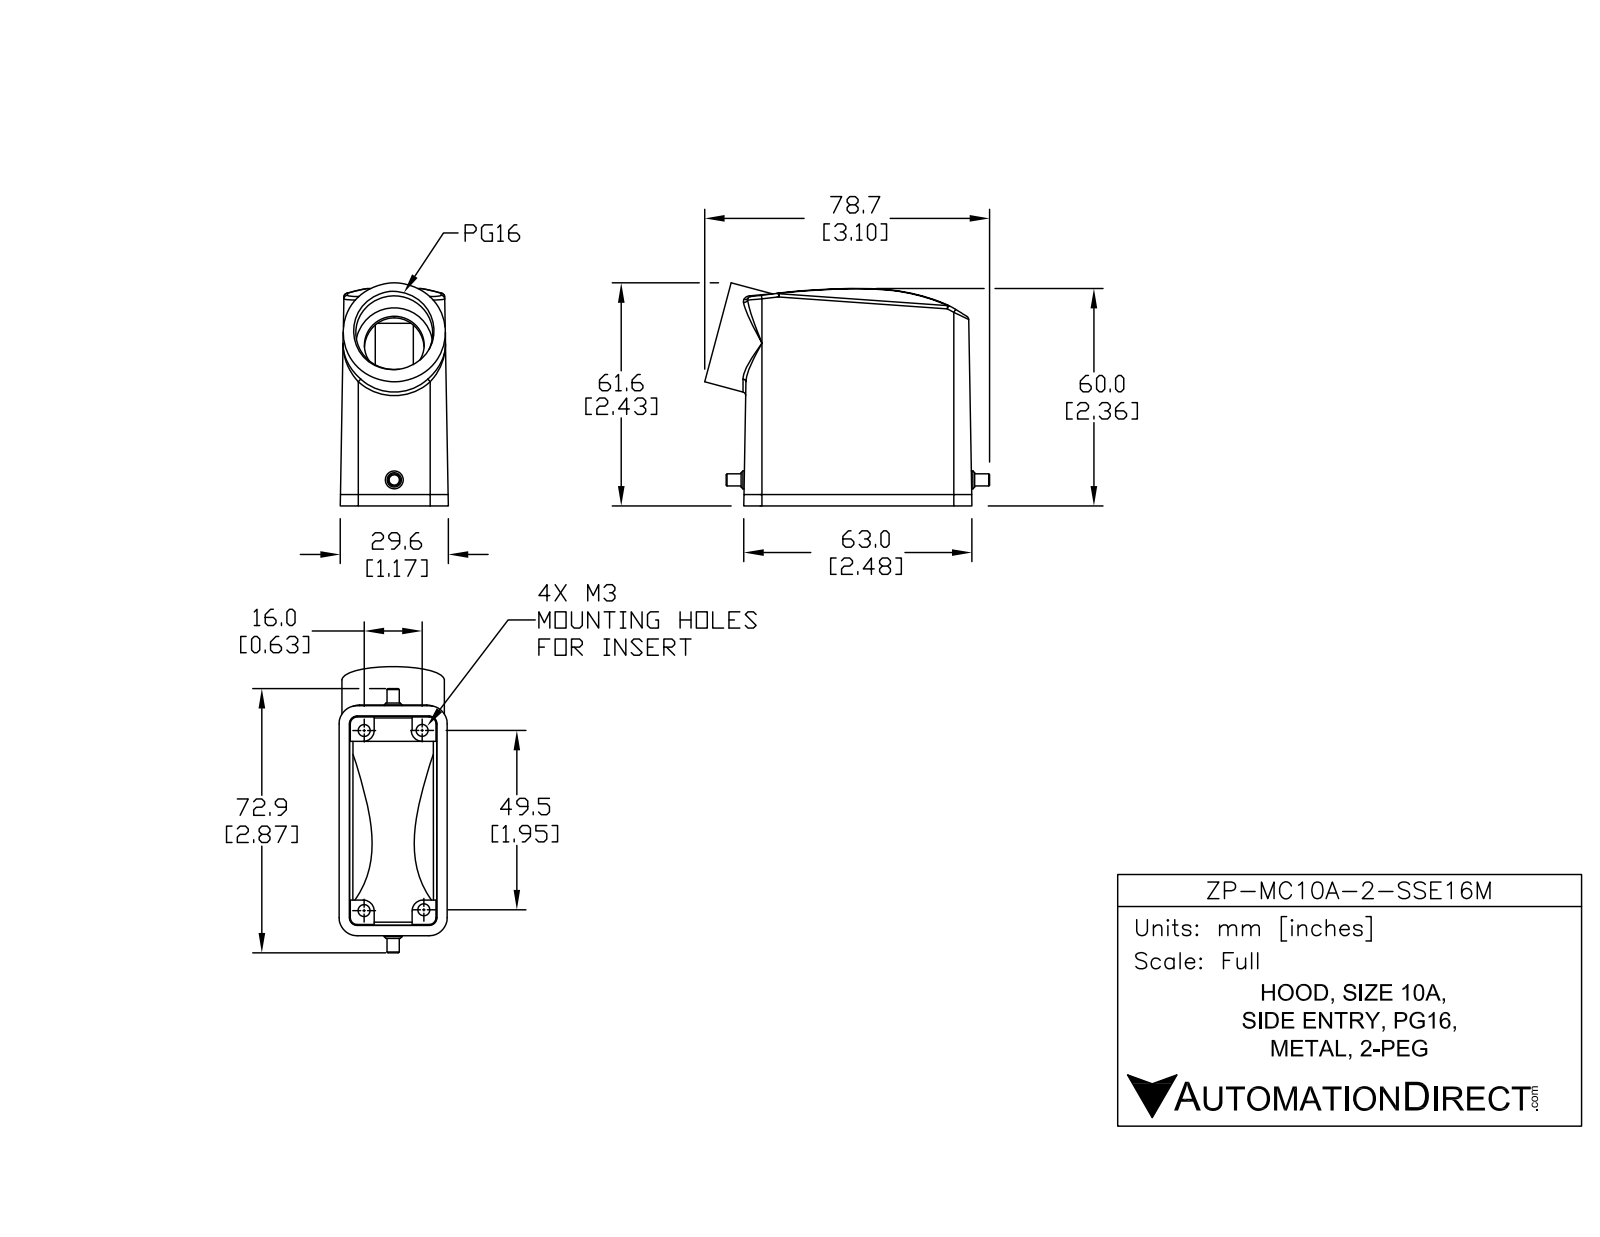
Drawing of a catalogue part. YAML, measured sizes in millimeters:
part_name: "ZP-MC10A-2-SSE16M"
step_written_by: "SolidWorks 2014 (AUTOMOTIVE_DESIGN)"
units: millimeters
bodies: {solids: 1, faces: 199, planar: 54, cylindrical: 85, other: 60}
overall_size: [79.15, 61.57, 29.6]
volume: 36633
surface_area: 24388
round_holes:
  - {diameter: 3, count: 4}
  - {diameter: 16.5, count: 1}
  - {diameter: 21.25, count: 1}
round_bosses_or_shafts:
  - {diameter: 28.03, count: 1}
  - {diameter: 4.95, count: 1}
  - {diameter: 3.35, count: 1}
partial_cylinders:
  - {radius: 1, count: 5}
  - {radius: 3, count: 4}
  - {radius: 25.65, count: 2}
  - {radius: 111.46, count: 2}
  - {radius: 124.56, count: 2}
  - {radius: 154.25, count: 2}
  - {radius: 155.71, count: 2}
  - {radius: 159.01, count: 2}
face_to_face_distances: [2.85, 2.63, 2.62, 43.5, 10, 13.7, 14.6, 2.61, 30.6, 16]
hole_center_spacings: [16, 49.5, 52.02]
